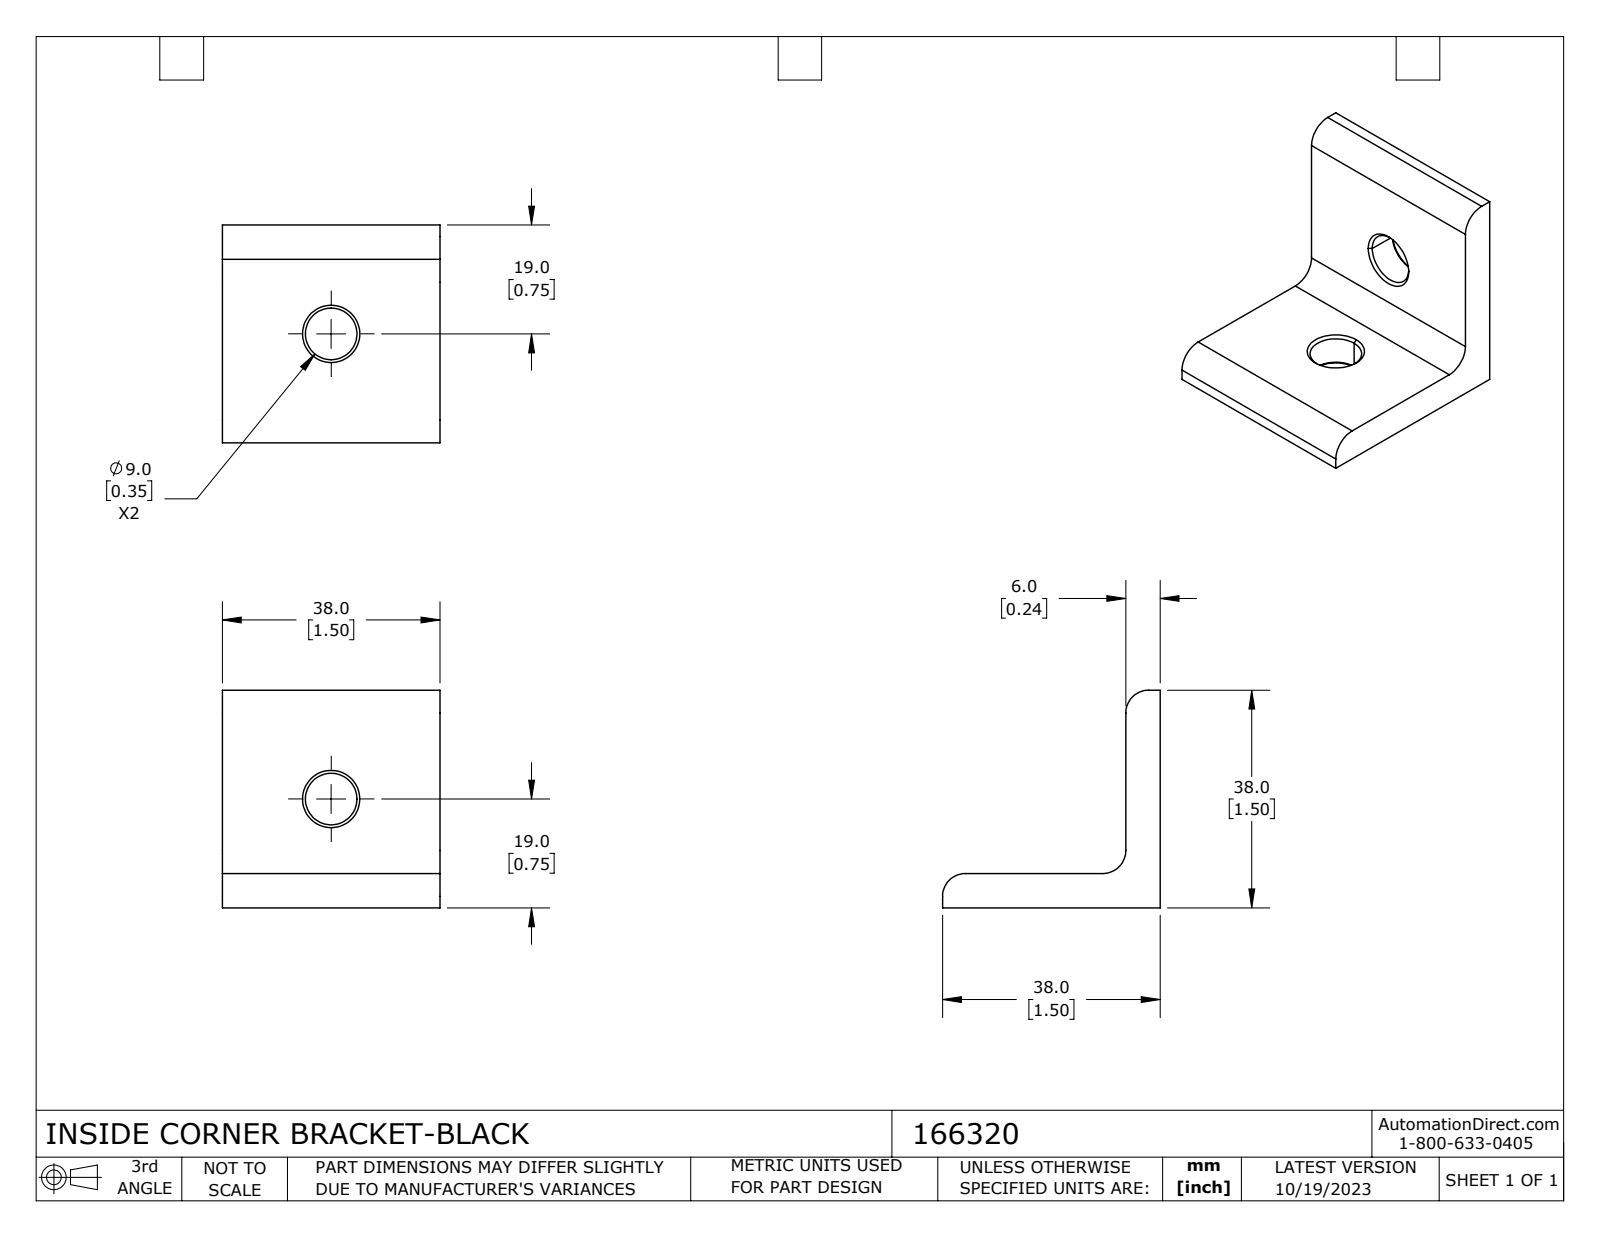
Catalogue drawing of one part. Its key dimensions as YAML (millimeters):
part_name: "166320"
step_written_by: "SolidWorks 2023 (CONFIG_CONTROL_DESIGN)"
units: millimeters
bodies: {solids: 1, faces: 23, planar: 8, cylindrical: 7, other: 8}
overall_size: [38, 38, 38]
volume: 15051
surface_area: 6466
round_holes:
  - {diameter: 9, count: 2}
partial_cylinders:
  - {radius: 4, count: 3}
face_to_face_distances: [6, 38, 32]
